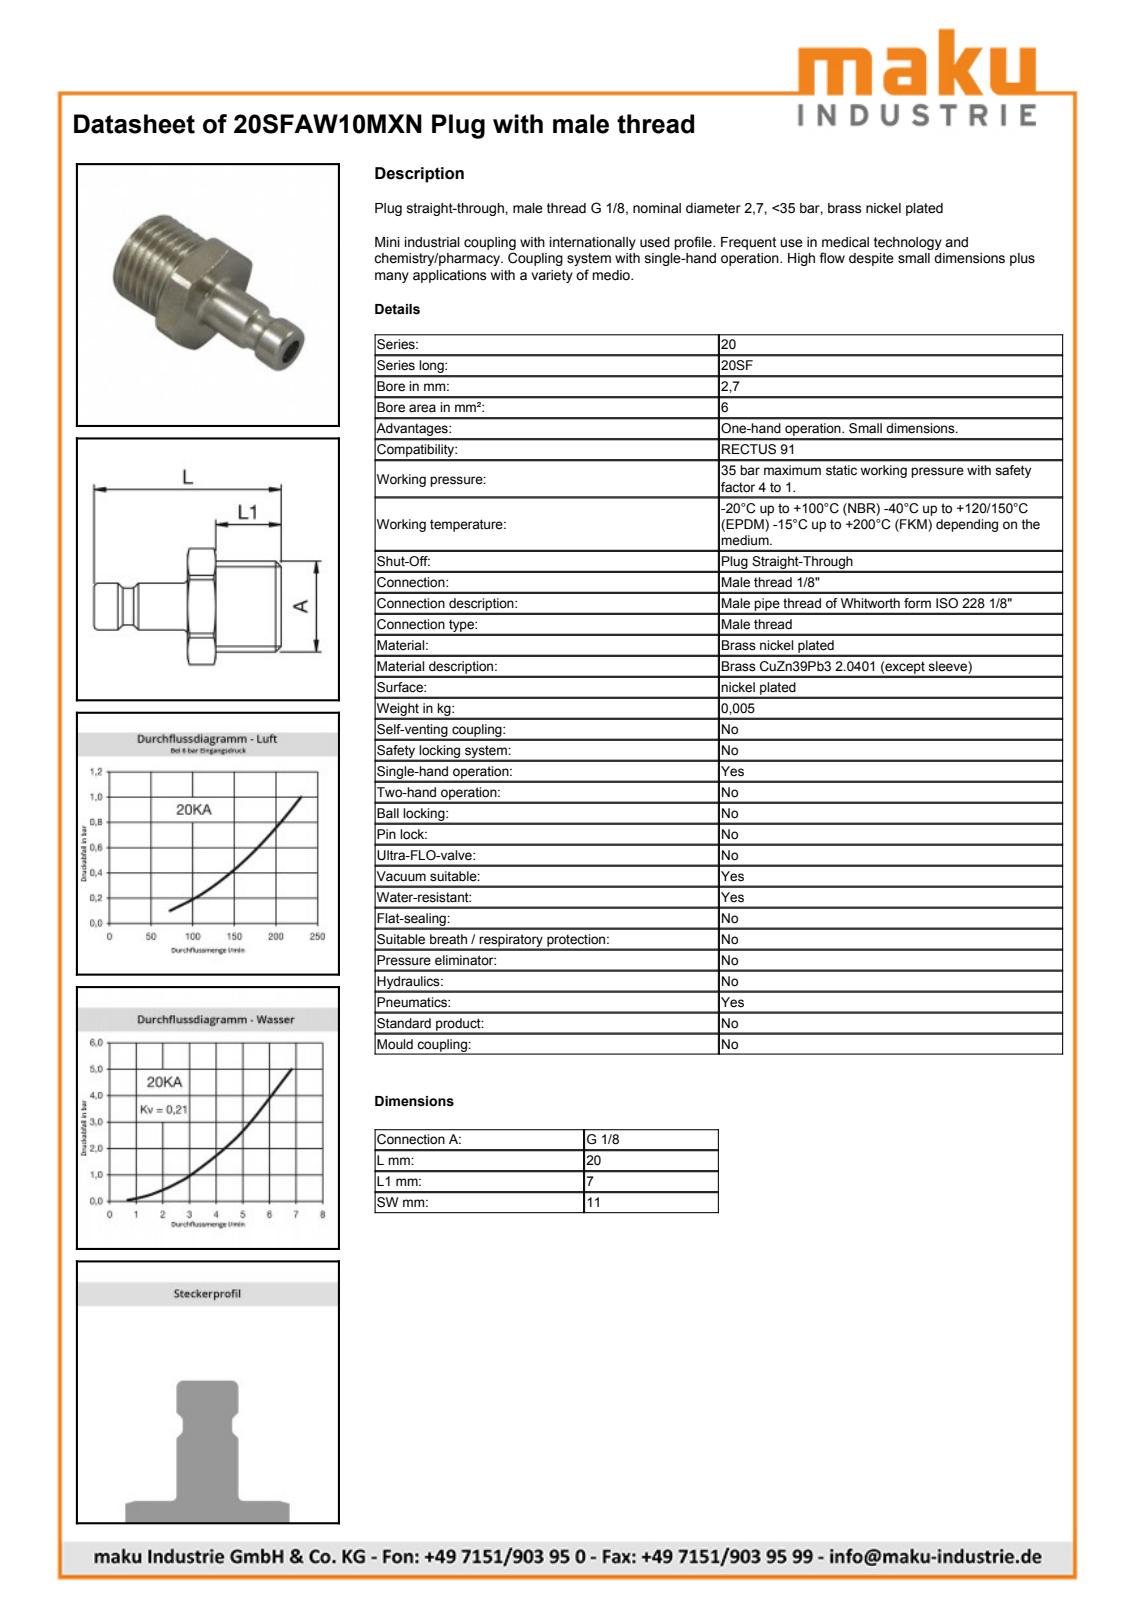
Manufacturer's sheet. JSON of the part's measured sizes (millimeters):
{"part_name": "D108792", "step_written_by": "Autodesk Inventor 2013 (AUTOMOTIVE_DESIGN)", "units": "millimeters", "bodies": {"solids": 1, "faces": 43, "planar": 10, "cylindrical": 12, "other": 21}, "overall_size": [20, 12.4, 11], "volume_mm3": 792, "surface_area_mm2": 921, "round_holes": [[2.7, 1], [6, 1]], "round_bosses_or_shafts": [[9.73, 1], [5, 1], [4, 1]], "partial_cylinders_radius": [[6.2, 1]], "face_to_face_distances": [11, 4.12, 11.12, 7, 8.88, 13, 20]}
